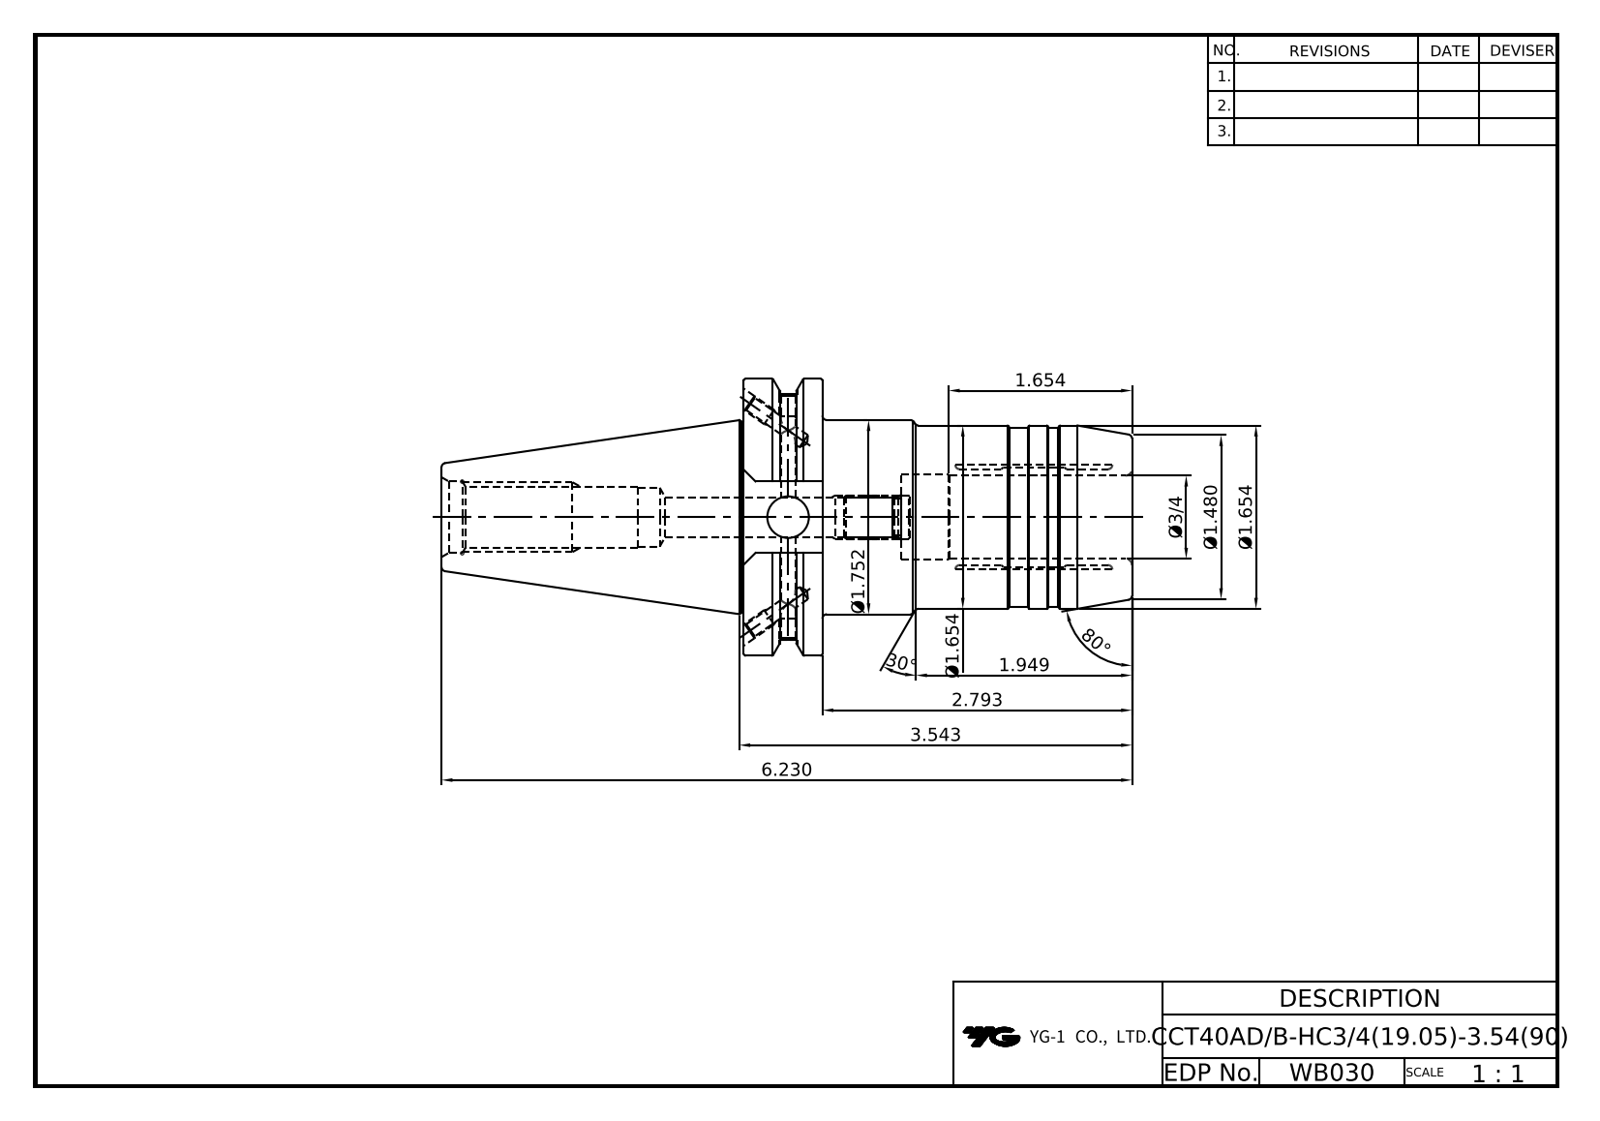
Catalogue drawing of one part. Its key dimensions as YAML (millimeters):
part_name: "CCT40ADB-HC19.05-90"
step_written_by: "Autodesk Inventor 2020 (AUTOMOTIVE_DESIGN)"
units: millimeters
bodies: {solids: 1, faces: 110, planar: 38, cylindrical: 34, other: 38}
overall_size: [158.25, 63.5, 61.09]
volume: 189766
surface_area: 33360
round_holes:
  - {diameter: 3.24, count: 4}
  - {diameter: 4, count: 2}
  - {diameter: 4.2, count: 2}
  - {diameter: 8.92, count: 1}
  - {diameter: 9.53, count: 1}
  - {diameter: 13, count: 1}
  - {diameter: 13.39, count: 1}
  - {diameter: 16.3, count: 1}
  - {diameter: 19.05, count: 1}
  - {diameter: 19.4, count: 1}
round_bosses_or_shafts:
  - {diameter: 63.5, count: 1}
  - {diameter: 44.5, count: 1}
  - {diameter: 43.8, count: 1}
  - {diameter: 42, count: 1}
  - {diameter: 41, count: 1}
partial_cylinders:
  - {radius: 28.15, count: 1}
face_to_face_distances: [18.05, 89, 70.95, 36, 17.95, 53, 47.6, 16.38, 69.25, 87.3]
